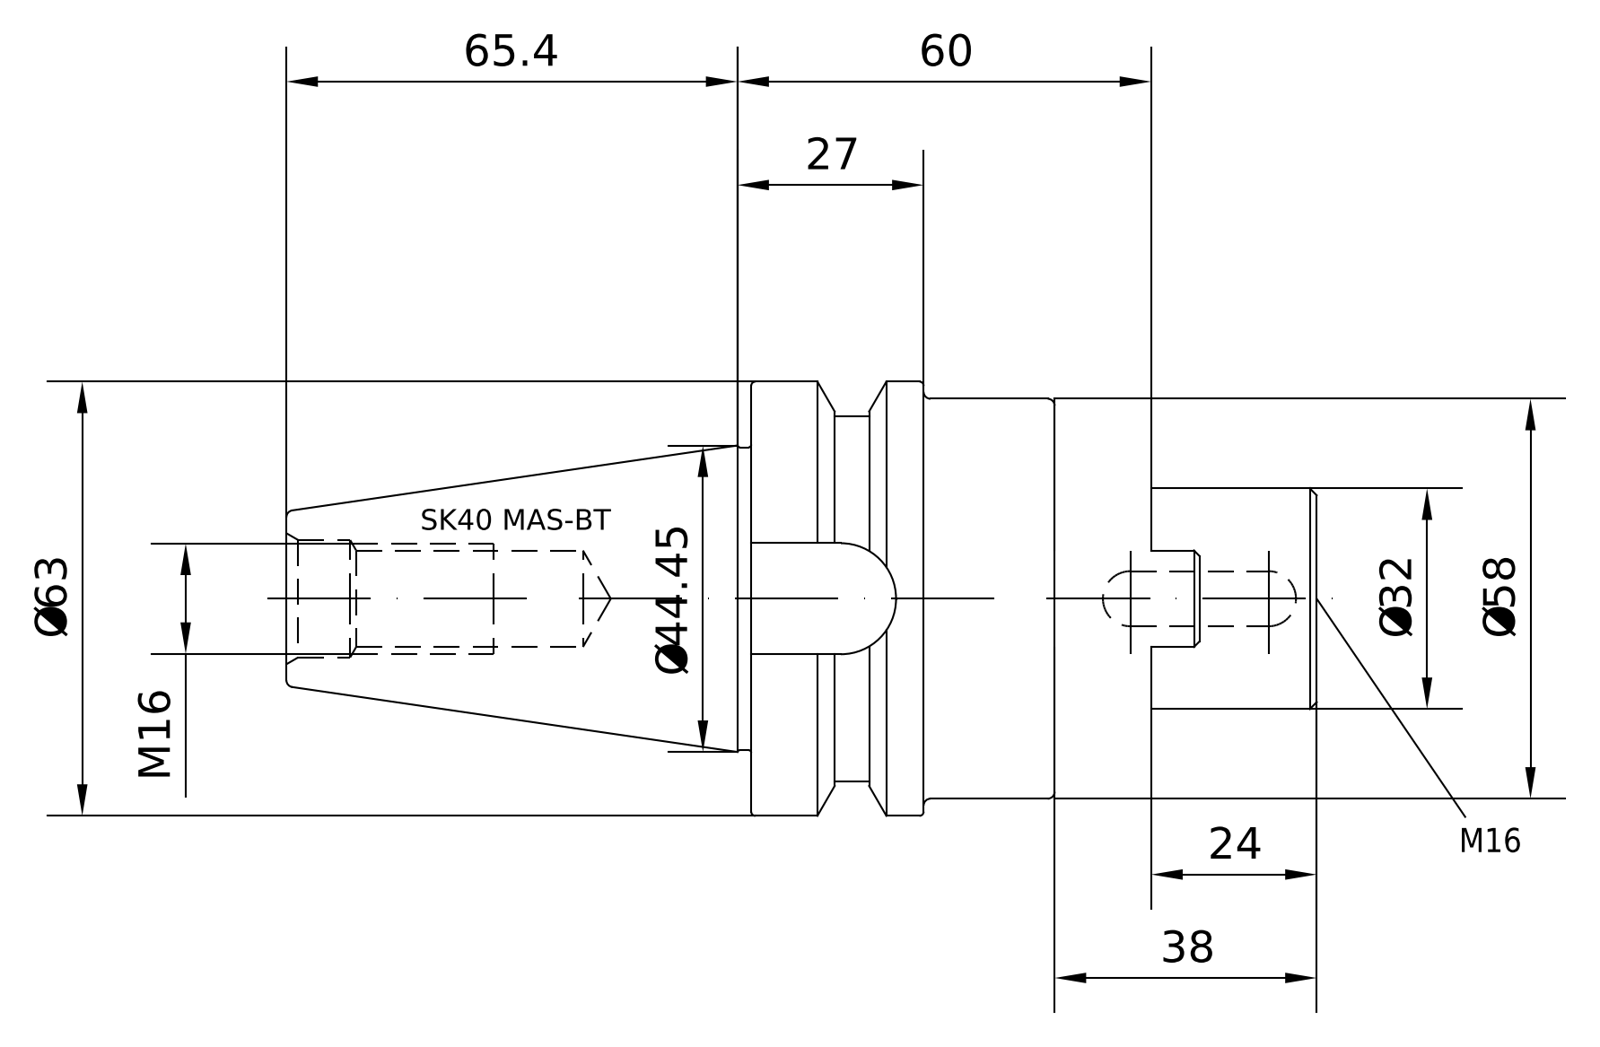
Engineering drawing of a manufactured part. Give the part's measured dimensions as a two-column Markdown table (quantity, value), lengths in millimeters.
| quantity | value |
| --- | --- |
| part name | 40-540-32; 85-200-32; 40-540-32_ASM |
| STEP written by | PRO/ENGINEER BY PARAMETRIC TECHNOLOGY CORPORATION, 2010430 (CONFIG_CONTROL_DESIGN) |
| units | millimeters |
| bodies | 2 solids, 188 faces (92 planar, 38 cylindrical, 58 other) |
| overall size | 149.4 × 62.98 × 62.98 |
| volume | 223 031 mm³ |
| surface area | 42 193 mm² |
| round holes (diameter × count) | 13.84 × 1, 14 × 1, 16 × 1, 17.01 × 1, 17.5 × 1, 32.39 × 1, 37 × 1 |
| round bosses / shafts (diameter × count) | 62.98 × 1, 58 × 1, 52.75 × 1, 43.75 × 1, 32 × 1, 16.01 × 1 |
| partial cylindrical surfaces (radius × count) | 4 × 2, 7.05 × 1, 8.1 × 1 |
| main face-to-face distances | 14, 44, 58, 82, 38, 24, 1, 13, 6.96, 7.96 |
